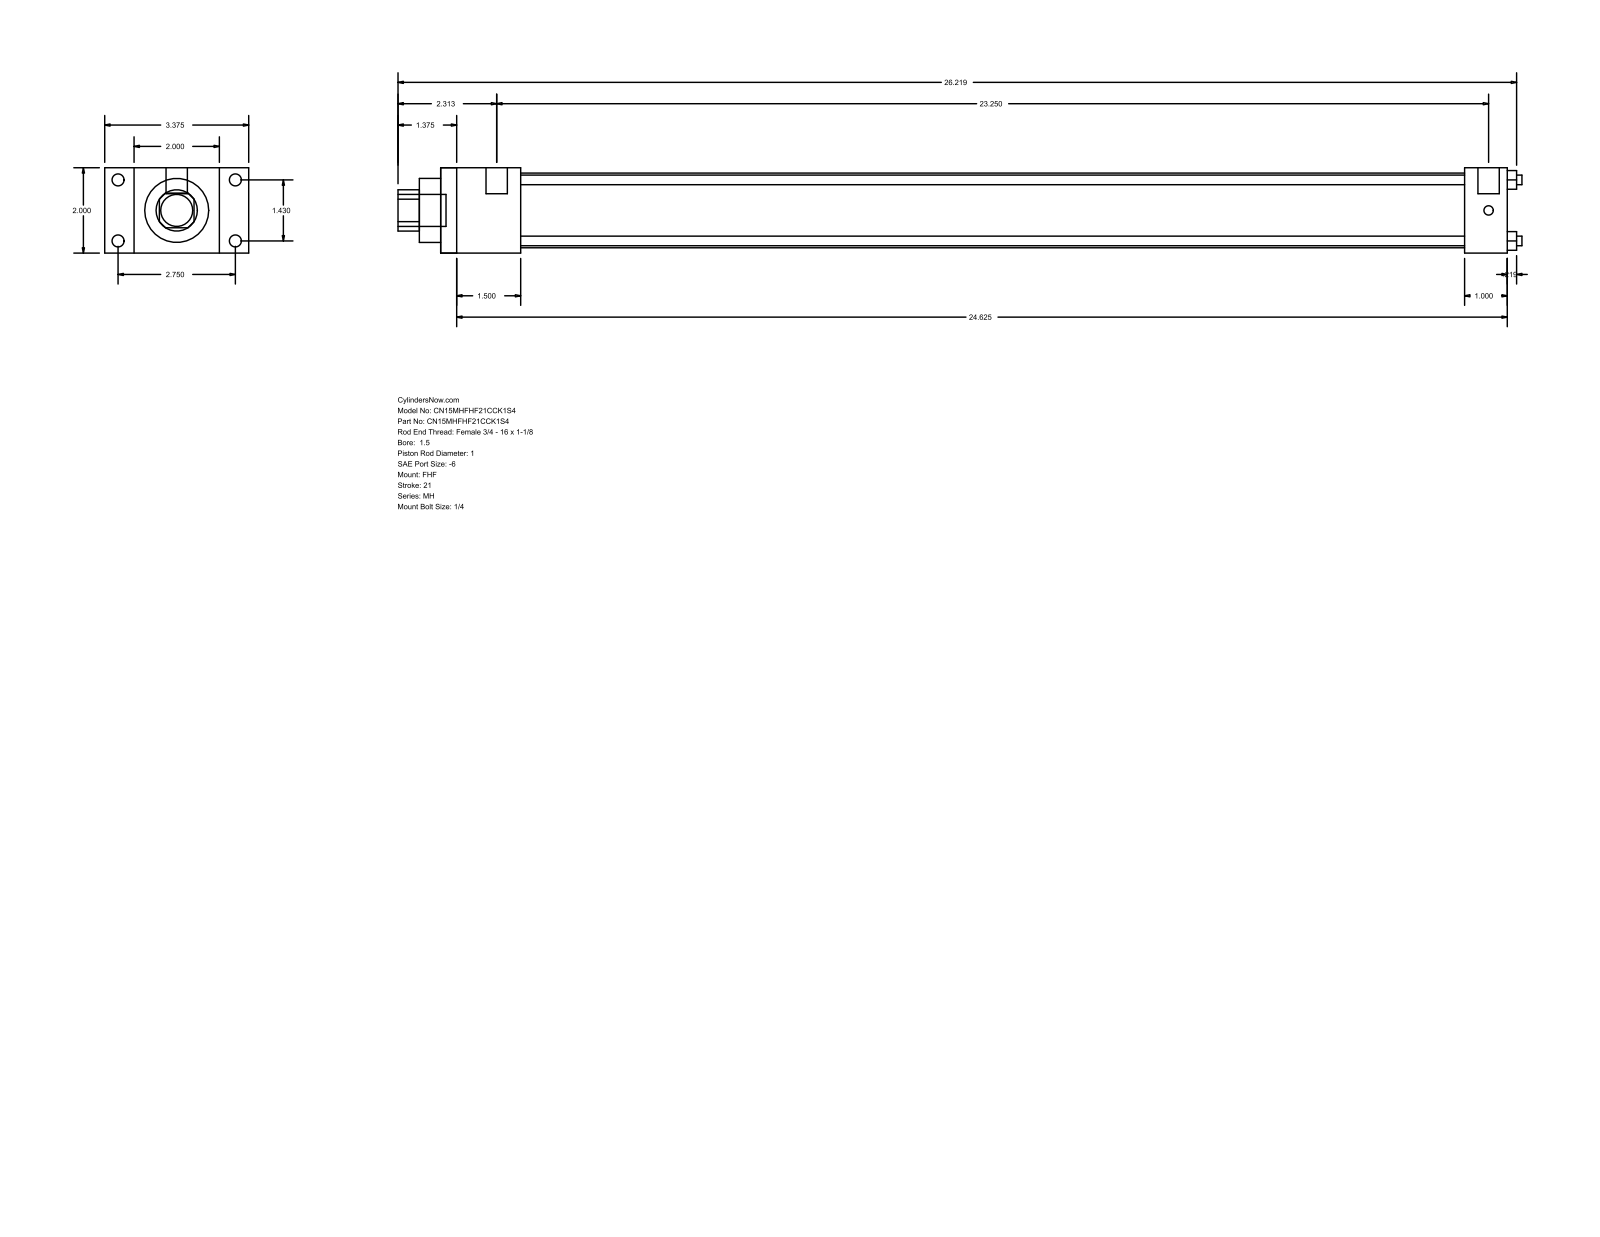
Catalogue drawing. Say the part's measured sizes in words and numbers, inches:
The part is named "MH_FHF__0150_1". Its 3-D file was written by "GSSL Pune (CONFIG_CONTROL_DESIGN)". It is 0 solids with 88 faces: 60 planar, 28 cylindrical and 0 other. Overall it measures 26.344 by 3.375 by 2 inches. Round holes: 4 of diameter 0.225, 1 of diameter 1, 1 of diameter 1.5, 1 of diameter 1.75. Round bosses or shafts: 4 of diameter 0.281, 4 of diameter 0.219, 2 of diameter 0.5, 1 of diameter 0.75. Partial cylindrical surfaces (rounded edges, fillets, slot ends): 1 of radius 0.484. The main face-to-face distances are 2, 0.687, 2.687, 1.875, 3.375, 25, 23.125, 1, 24, 22.125. The hole center spacings are 1.011, 1.43, 2.022.
